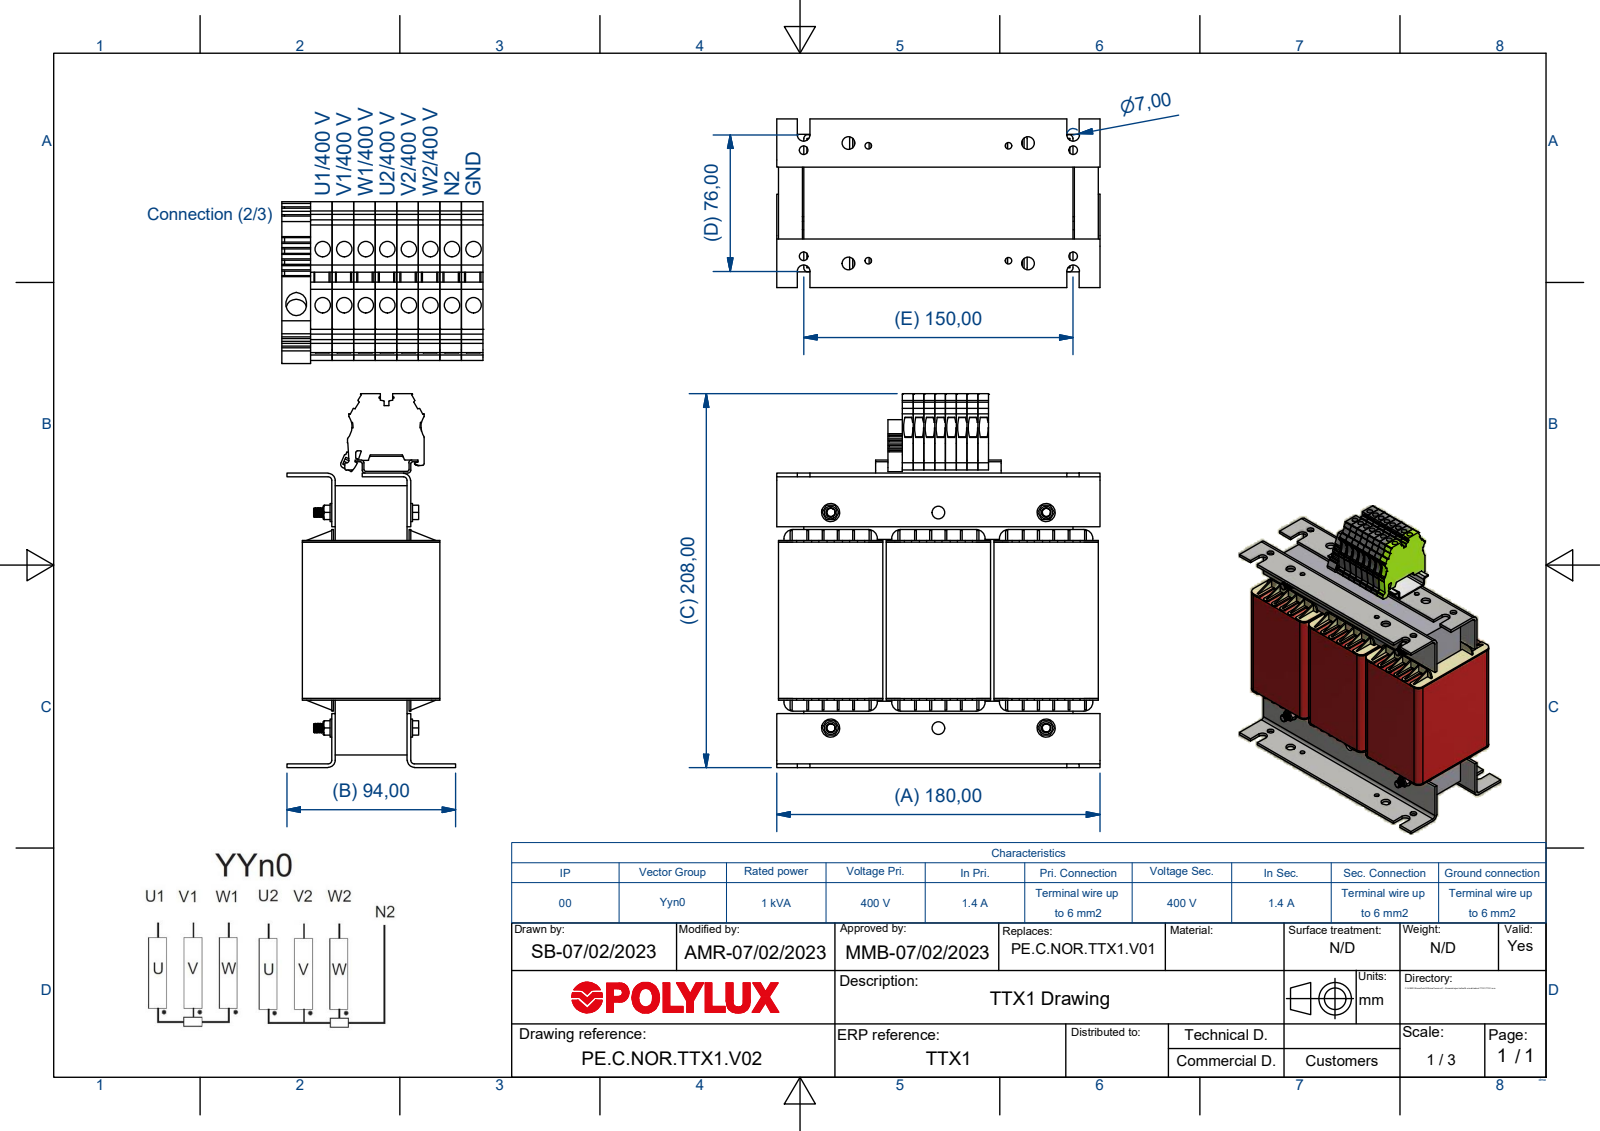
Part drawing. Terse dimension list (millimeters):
name: TTX1_bien; Núcleo RC30x30; BRI30-3IP02; 7xBOR0046+TIERRA (+8 more)
written by: Autodesk Inventor 2018 (AUTOMOTIVE_DESIGN)
unit: mm
bodies: 38 solids, 2476 faces (1724 planar, 728 cylindrical, 24 other)
size: 208.31 × 180 × 84
volume: 1 428 000 mm³; area: 440 360 mm²
holes: 16× ⌀4.3, 12× ⌀7, 6× ⌀3.5, 6× ⌀4.92, 4× ⌀4.13, 4× ⌀5.3, 4× ⌀6, 2× ⌀3, 2× ⌀5.8
bosses: 4× ⌀10, 4× ⌀5
rounds: 33× R0.5, 24× R2.25, 16× R24.01, 13× R0.1, 12× R0.3, 12× R1, 12× R4.65, 12× R5
face distances: 2, 60, 1, 32, 46, 1.25, 2.25, 32.25, 120, 30
hole spacings: 6, 16.71, 12, 19.68, 32, 11.1, 15.6, 18
